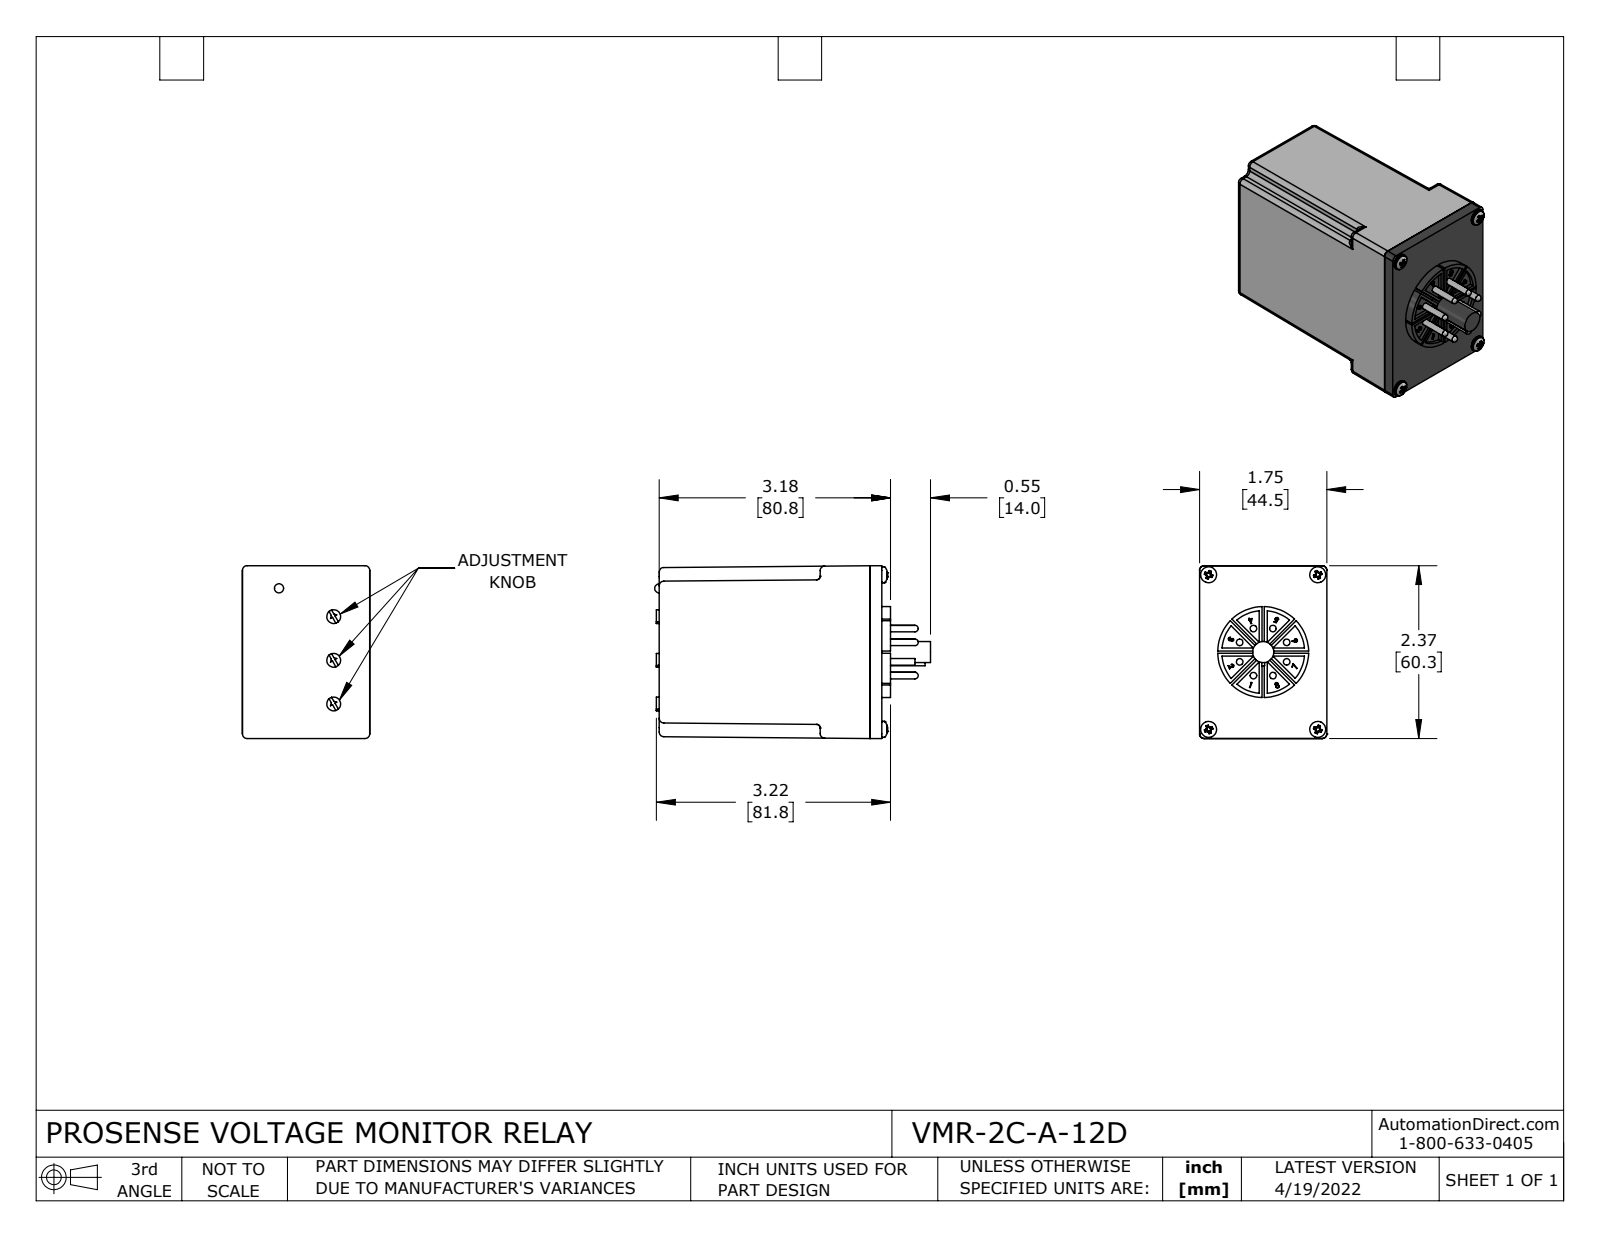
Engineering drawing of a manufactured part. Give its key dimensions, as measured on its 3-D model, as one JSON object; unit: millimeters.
{"part_name": "VMR-2C-A-12D", "step_written_by": "SolidWorks 2021 (CONFIG_CONTROL_DESIGN)", "units": "millimeters", "bodies": {"solids": 18, "faces": 574, "planar": 249, "cylindrical": 170, "other": 155}, "overall_size": [96.3, 60.3, 44.5], "volume_mm3": 200700, "surface_area_mm2": 28850, "round_holes": [[3.2, 4]], "round_bosses_or_shafts": [[2.3, 8], [5.6, 4], [4.8, 3], [31.8, 1], [7.4, 1]], "partial_cylinders_radius": [[1.6, 32], [0.1, 8], [1.3, 4], [14.5, 1]], "face_to_face_distances": [73.7, 4.1, 77.7, 1.8, 5.8, 79.5, 4.8, 1.3, 3, 7.1], "hole_center_spacings": [38.1, 54, 66.1]}
